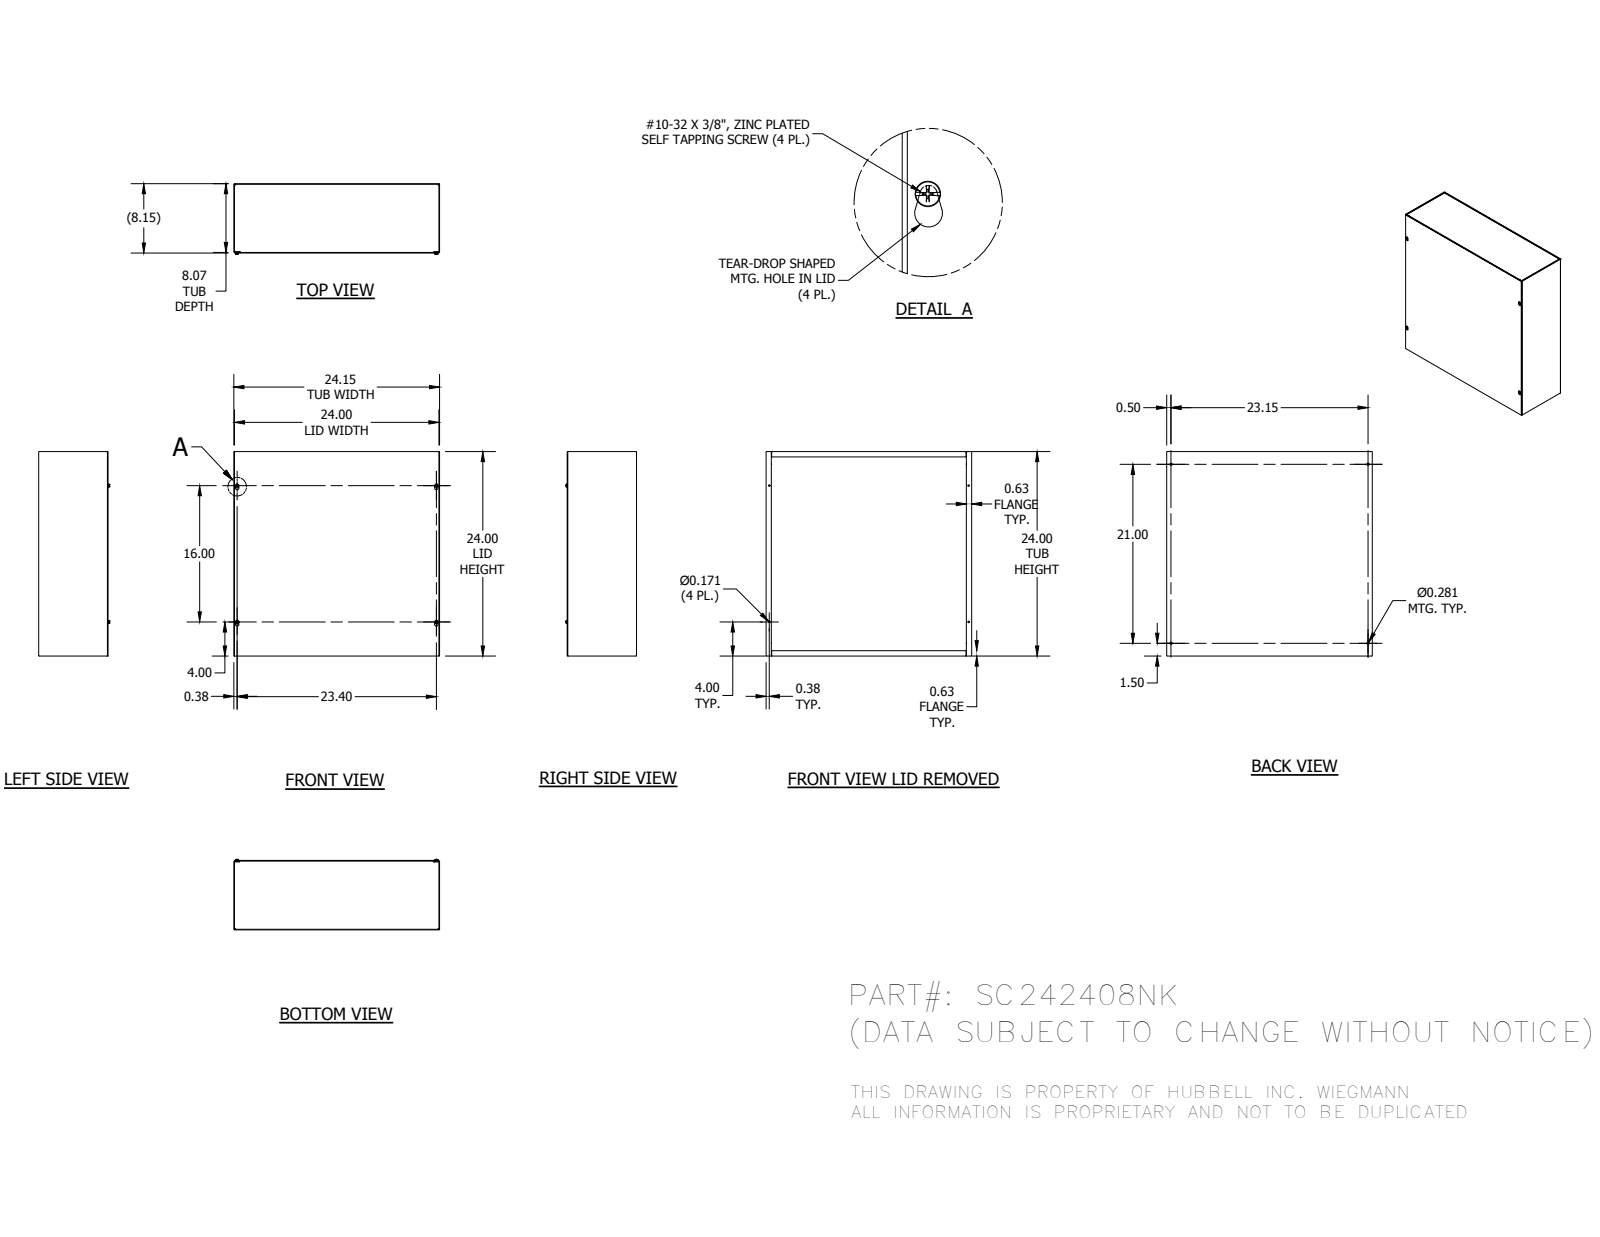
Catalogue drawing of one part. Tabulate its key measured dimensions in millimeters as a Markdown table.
| quantity | value |
| --- | --- |
| part name | SC242408NKBLR; SC2408NKTB; SC2424LPA; 37214 (+1 more) |
| STEP written by | Autodesk Inventor 2014 (AUTOMOTIVE_DESIGN) |
| units | millimeters |
| bodies | 8 solids, 320 faces (192 planar, 44 cylindrical, 84 other) |
| overall size | 613.36 × 609.6 × 210.31 |
| volume | 2 442 000 mm³ |
| surface area | 2 616 000 mm² |
| round holes (diameter × count) | 4.34 × 4, 7.14 × 4 |
| round bosses / shafts (diameter × count) | 4.83 × 4 |
| partial cylindrical surfaces (radius × count) | 0.4 × 12, 2.28 × 12, 3.17 × 4, 5.16 × 4 |
| main face-to-face distances | 1.88, 205.08, 203.2, 206.96, 609.6, 607.72, 611.48, 605.84, 613.36, 3.76 |
| hole center spacings | 63.58, 469.91, 594.53, 755.14, 406.4, 533.4, 587.96, 594.3 |
